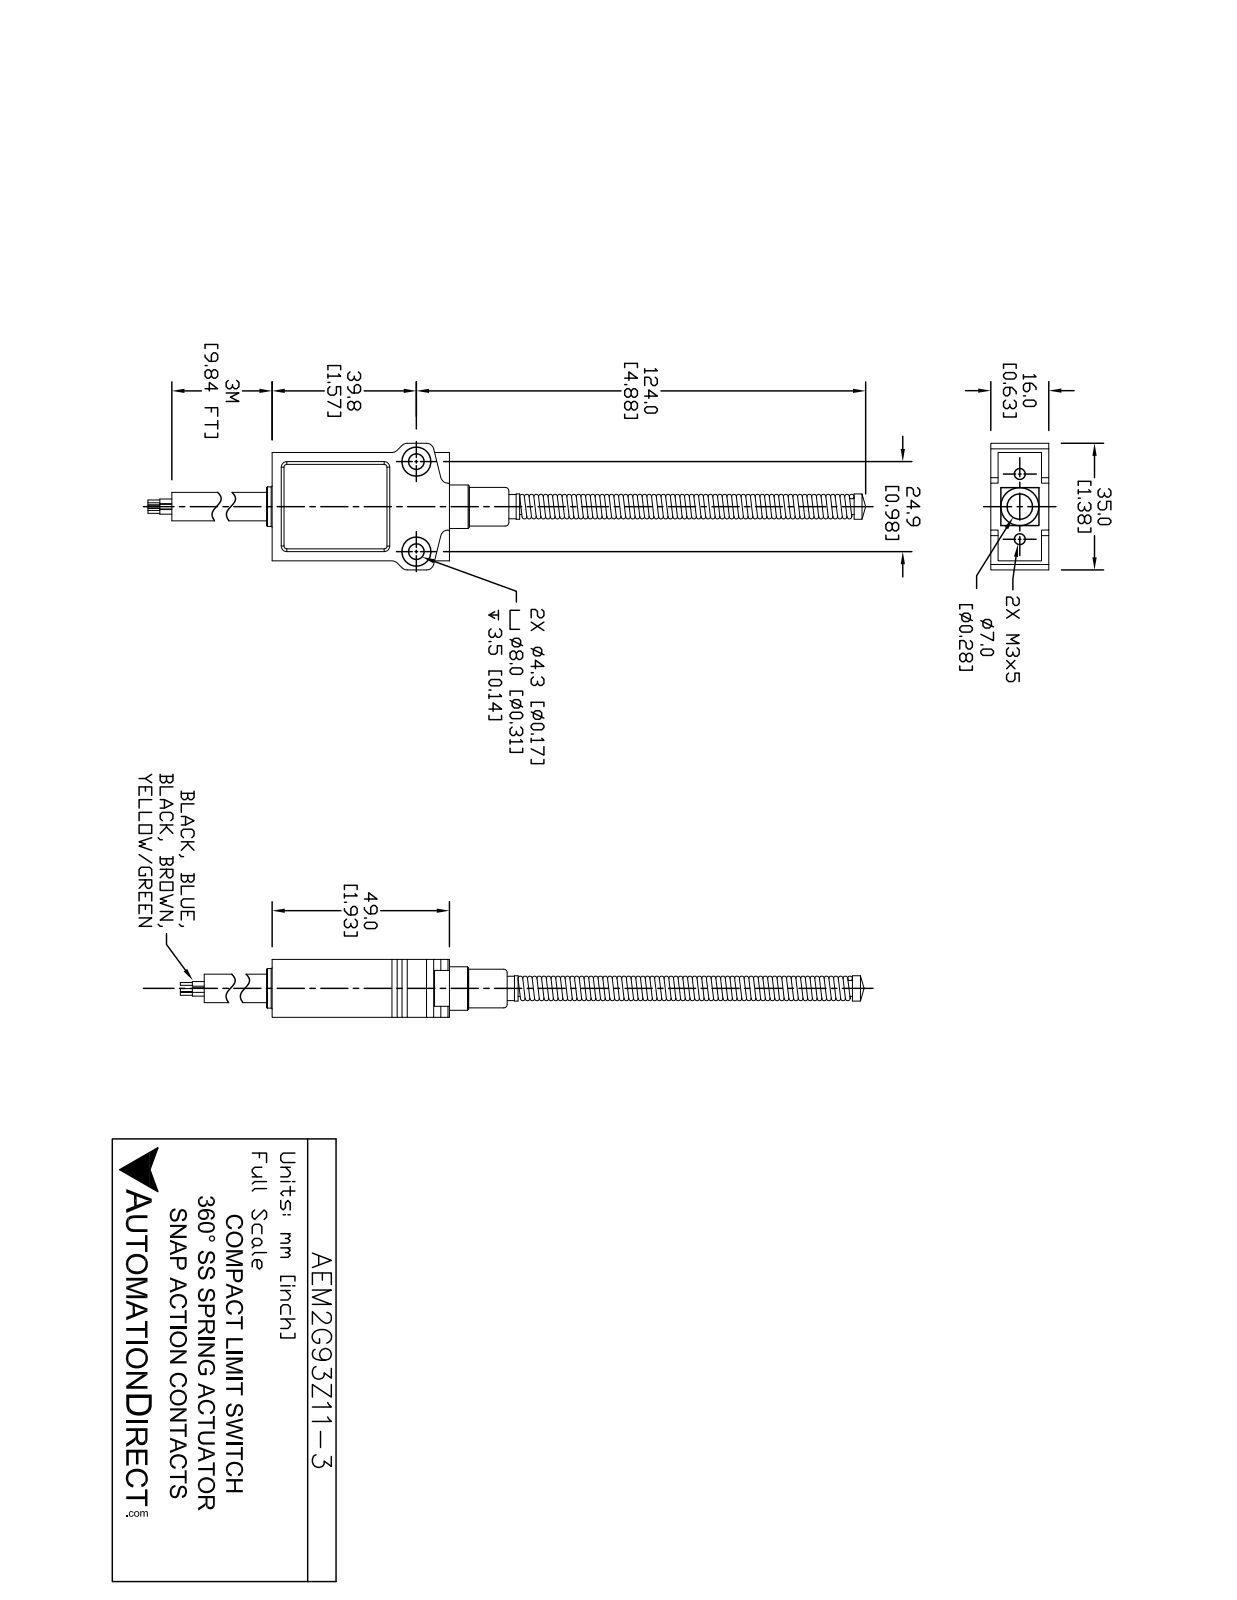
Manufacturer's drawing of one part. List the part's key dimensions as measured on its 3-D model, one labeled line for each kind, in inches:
Part name (STEP PRODUCT): AEM2G93Z11-3_Default
STEP written by: SolidWorks 2021 (CONFIG_CONTROL_DESIGN)
Units: inches
Bodies: 3 solids, 121 faces (52 planar, 50 cylindrical, 19 other)
Overall size (bounding box): 7.031 × 1.378 × 0.63
Volume: 1.769 in³ · Surface area: 15.57 in²
Round holes (diameter × count): ⌀0.118 ×2, ⌀0.173 ×2, ⌀0.323 ×2
Round bosses / shafts (diameter × count): ⌀0.472 ×1, ⌀0.433 ×1, ⌀0.315 ×1, ⌀0.276 ×1, ⌀0.268 ×1, ⌀0.232 ×1
Partial cylindrical surfaces — rounded edges, fillets, slot ends (radius × count): R0.079 ×8, R0.119 ×1, R0.119 ×1, R0.256 ×1
Main face-to-face distances: 0.63, 1.181, 1.929, 0.472, 1.74, 0.189, 0.098, 1.28, 0.157, 0.512
Hole centre spacings: 0.748, 0.984
